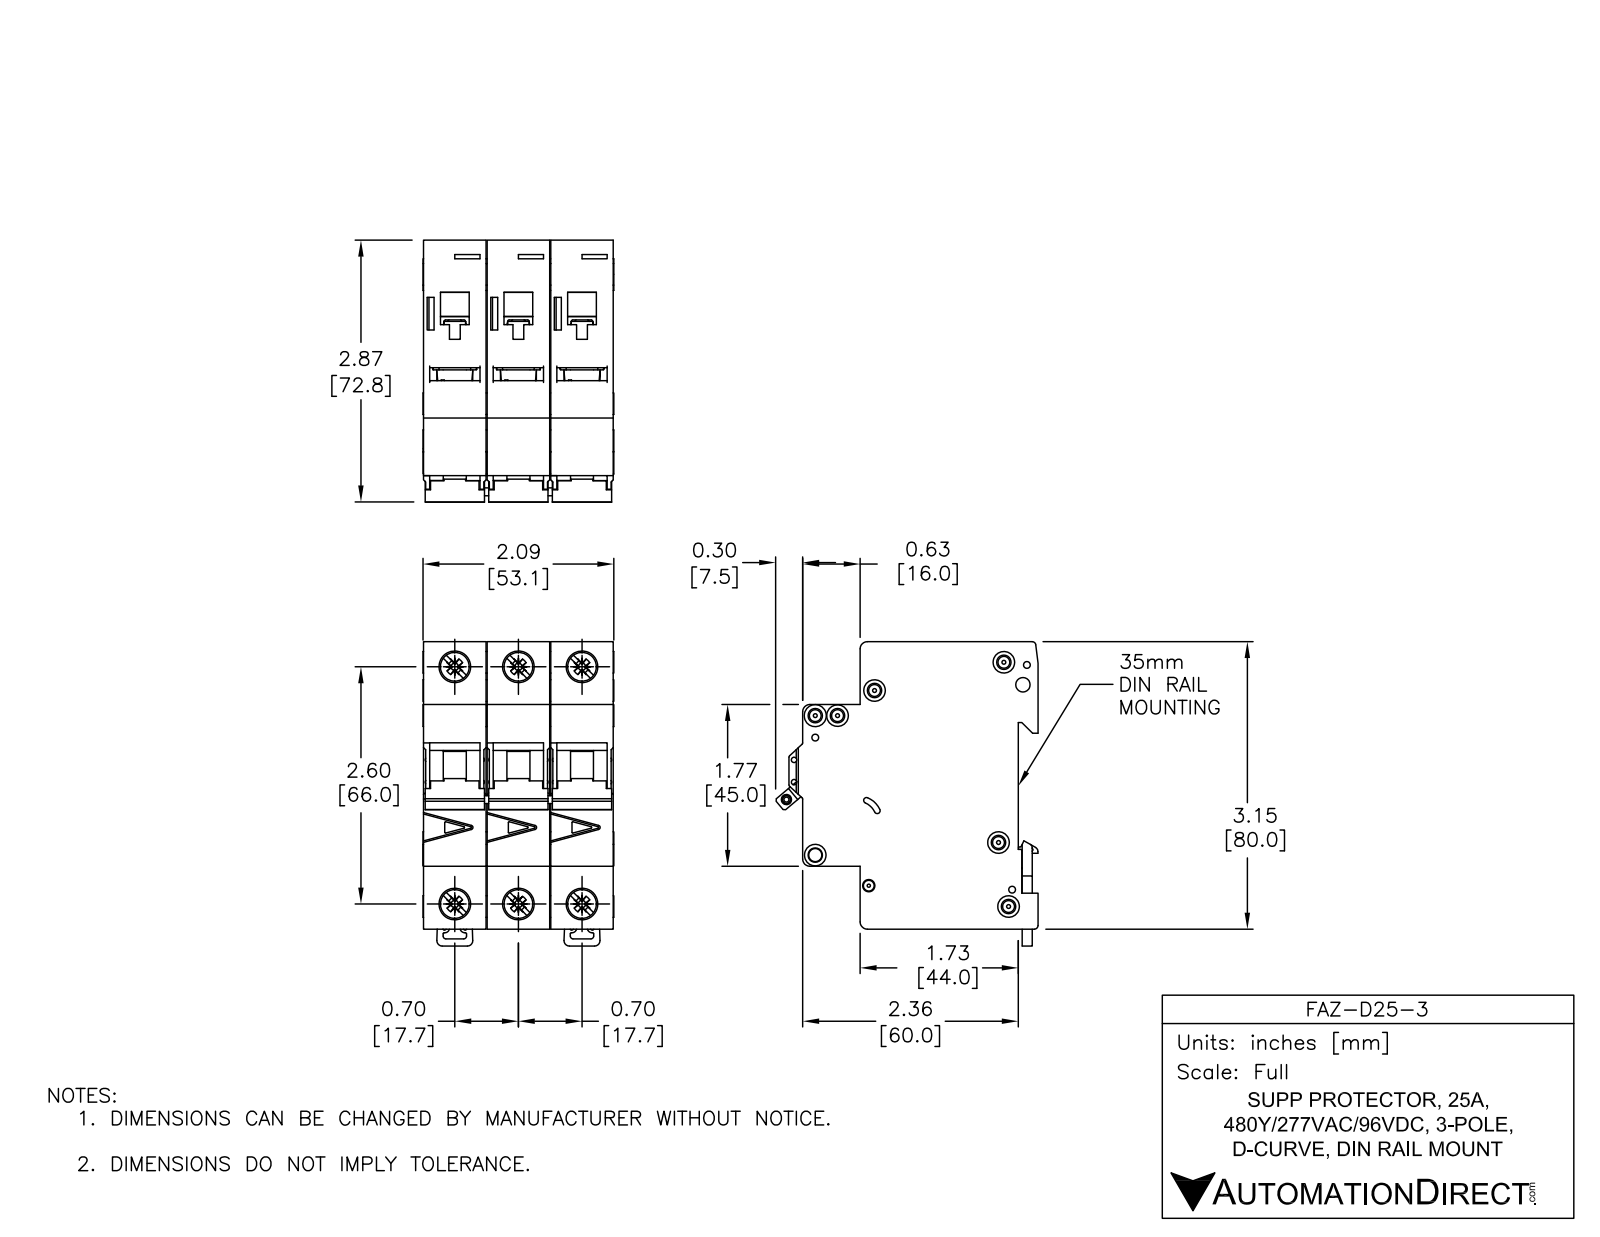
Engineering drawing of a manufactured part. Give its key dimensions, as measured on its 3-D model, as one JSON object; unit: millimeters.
{"part_name": "FAZ-D25-3", "step_written_by": "SolidWorks 2014 (AUTOMOTIVE_DESIGN)", "units": "millimeters", "bodies": {"solids": 11, "faces": 1650, "planar": 697, "cylindrical": 590, "other": 363}, "overall_size": [84.78, 73.04, 53.1], "volume_mm3": 224680, "surface_area_mm2": 58052, "round_holes": [[3.6, 6], [8.2, 4], [1.9, 3], [1.09, 2], [1.5, 2], [4, 2], [7.15, 2], [2.15, 1], [2.2, 1], [2.55, 1], [3.3, 1], [3.4, 1]], "round_bosses_or_shafts": [[6, 4], [2.5, 3], [8.2, 2]], "partial_cylinders_radius": [[0.25, 68], [0.5, 25], [1, 12], [2, 12], [0.2, 11], [1.8, 3], [0.8, 2], [3, 2]], "face_to_face_distances": [17.7, 17.5, 35.4, 35.2, 52.9, 17.9, 79.48, 5.5, 49.5, 44], "hole_center_spacings": [17.7, 68.33, 66, 6.2, 13.64, 35.4, 74.89, 4.81]}
